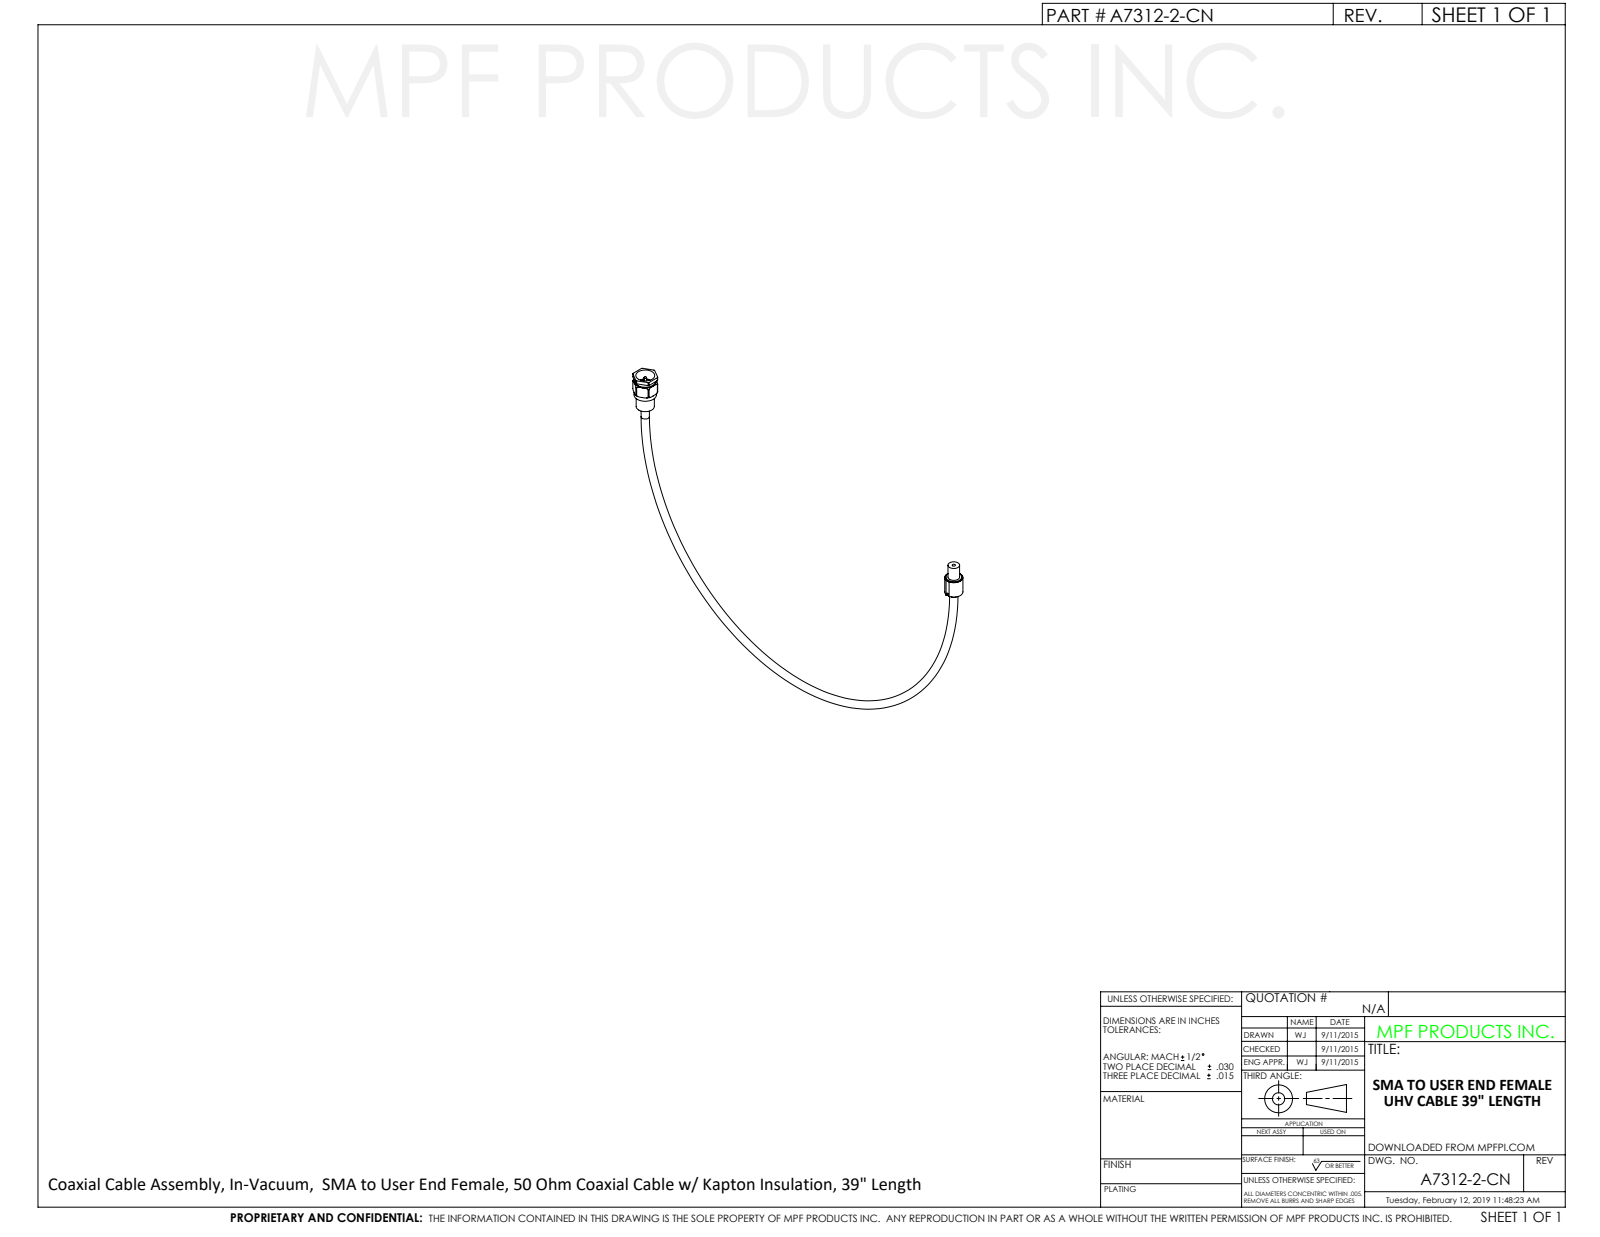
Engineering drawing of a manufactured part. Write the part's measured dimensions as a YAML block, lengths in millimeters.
part_name: "A7311-2-CN"
step_written_by: "SolidWorks 2012 (CONFIG_CONTROL_DESIGN)"
units: millimeters
bodies: {solids: 3, faces: 138, planar: 45, cylindrical: 55, other: 38}
overall_size: [159.5, 95.3, 8.9]
volume: 2280
surface_area: 3583
round_holes:
  - {diameter: 1.1, count: 1}
  - {diameter: 1.3, count: 1}
  - {diameter: 2.9, count: 1}
  - {diameter: 4.2, count: 1}
  - {diameter: 6.1, count: 1}
  - {diameter: 6.6, count: 1}
  - {diameter: 7.4, count: 1}
round_bosses_or_shafts:
  - {diameter: 6.4, count: 2}
  - {diameter: 7.8, count: 1}
  - {diameter: 7.1, count: 1}
  - {diameter: 5.6, count: 1}
  - {diameter: 4.9, count: 1}
  - {diameter: 4.6, count: 1}
  - {diameter: 4.2, count: 1}
  - {diameter: 4.1, count: 1}
partial_cylinders:
  - {radius: 4.4, count: 1}
face_to_face_distances: [7.9, 6.2, 3.1, 10.1, 7, 16.3, 13.2, 4.9, 0.7, 0.6]
hole_center_spacings: [152.4]
